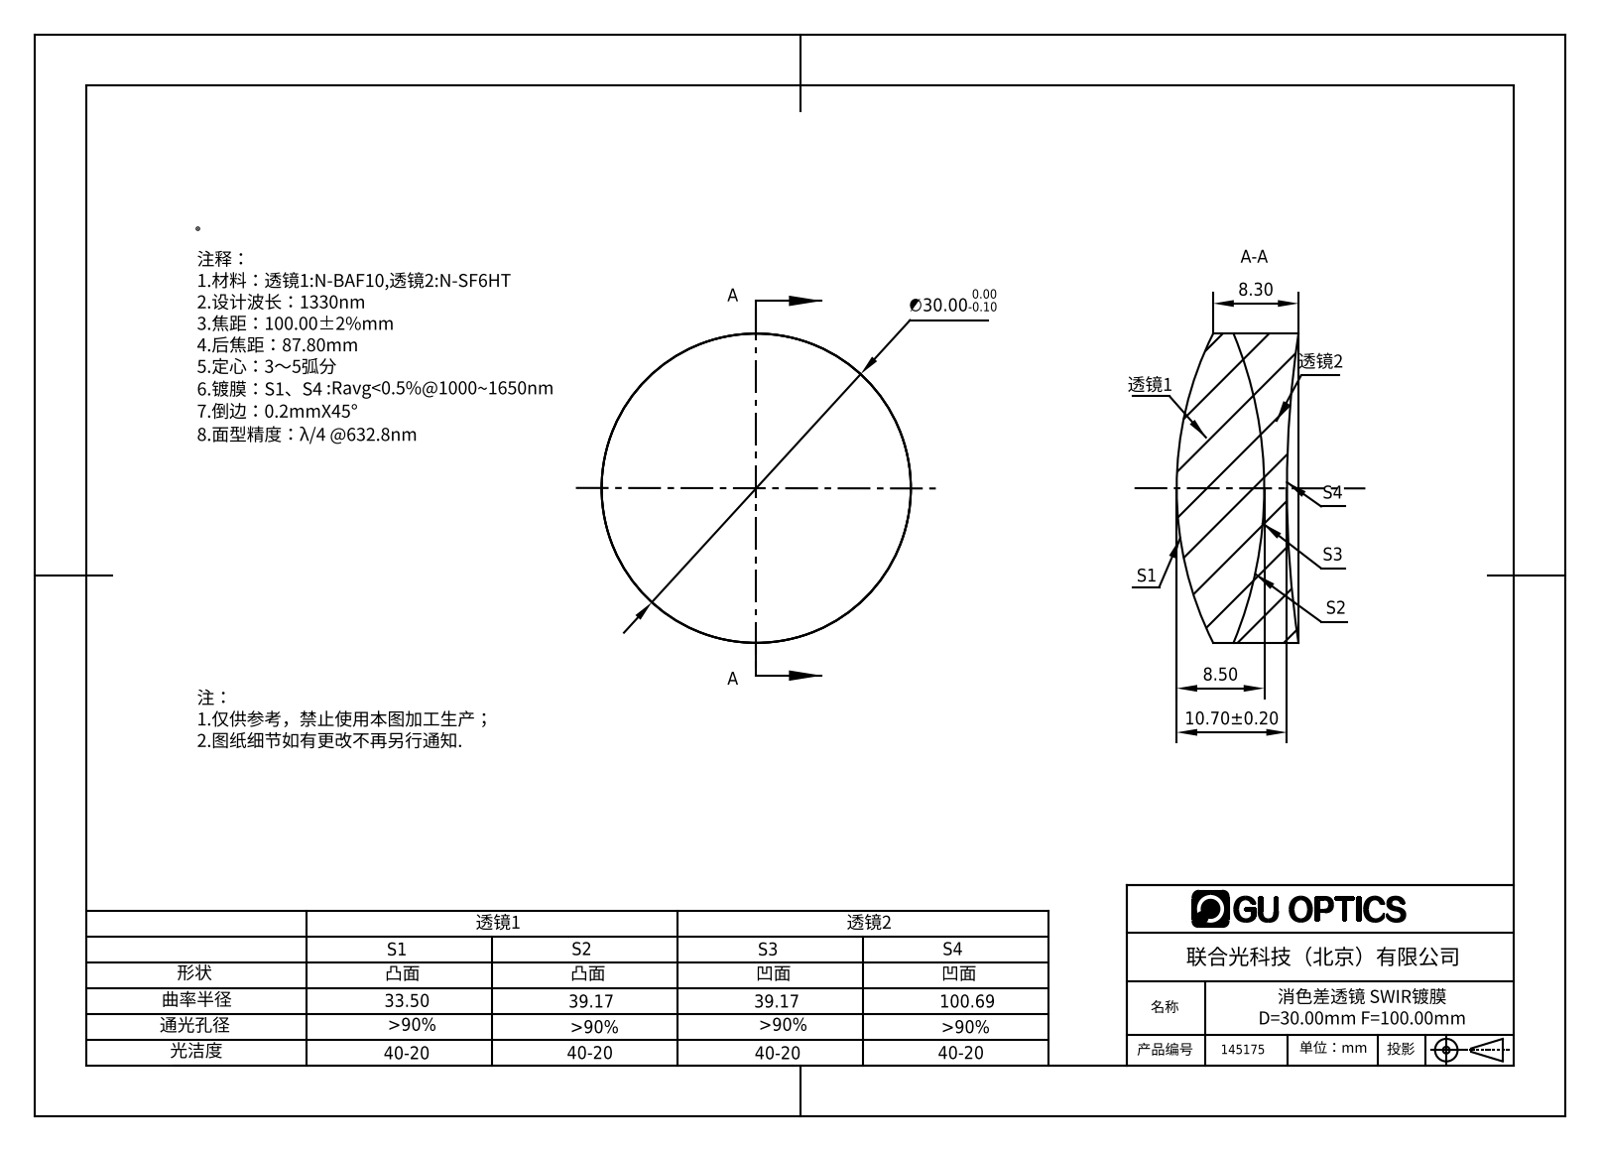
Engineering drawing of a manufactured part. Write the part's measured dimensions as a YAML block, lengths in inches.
part_name: "145175"
step_written_by: "SolidWorks 2016 (AUTOMOTIVE_DESIGN)"
units: inches
bodies: {solids: 2, faces: 12, planar: 0, cylindrical: 4, other: 8}
overall_size: [1.181, 1.181, 0.465]
volume: 0.411
surface_area: 5.746
round_bosses_or_shafts:
  - {diameter: 1.181, count: 1}
